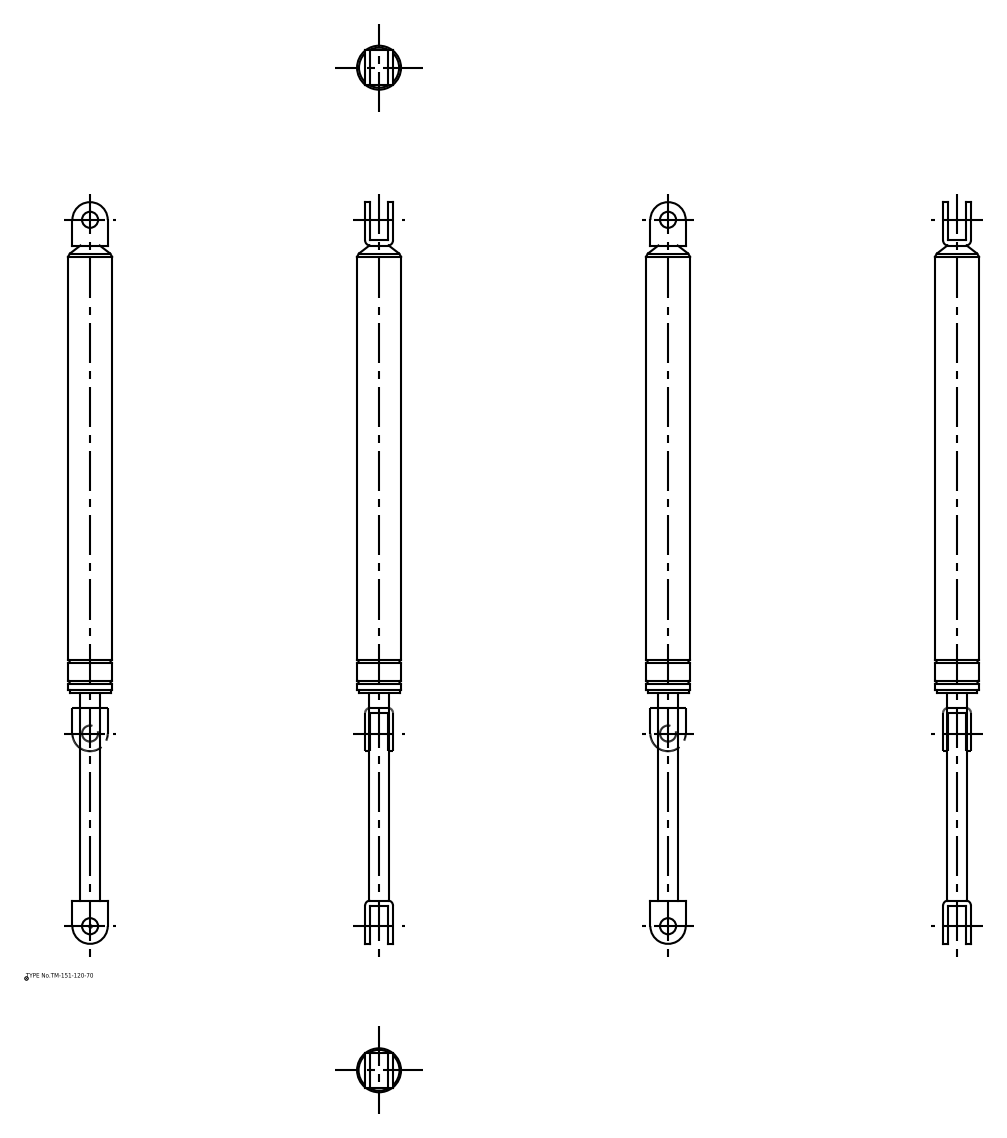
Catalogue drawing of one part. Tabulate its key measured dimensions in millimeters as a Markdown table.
| quantity | value |
| --- | --- |
| part name | TM_151_120_70; TM_151_120_70_div |
| STEP written by | spGate 16.7.1 (AUTOMOTIVE_DESIGN) |
| units | millimeters |
| bodies | 2 solids, 64 faces (22 planar, 32 cylindrical, 10 other) |
| overall size | 462 × 28.2 × 28.2 |
| volume | 186 044 mm³ |
| surface area | 35 864 mm² |
| round holes (diameter × count) | 10 × 2 |
| round bosses / shafts (diameter × count) | 28.2 × 1, 27.4 × 1, 25.5 × 1, 12.5 × 1 |
| partial cylindrical surfaces (radius × count) | 3.2 × 4, 11 × 2 |
| main face-to-face distances | 3.2, 14.2, 17.4, 11, 22, 411.2, 132.2, 414.4, 282.2, 279 |
| hole center spacings | 440 |
